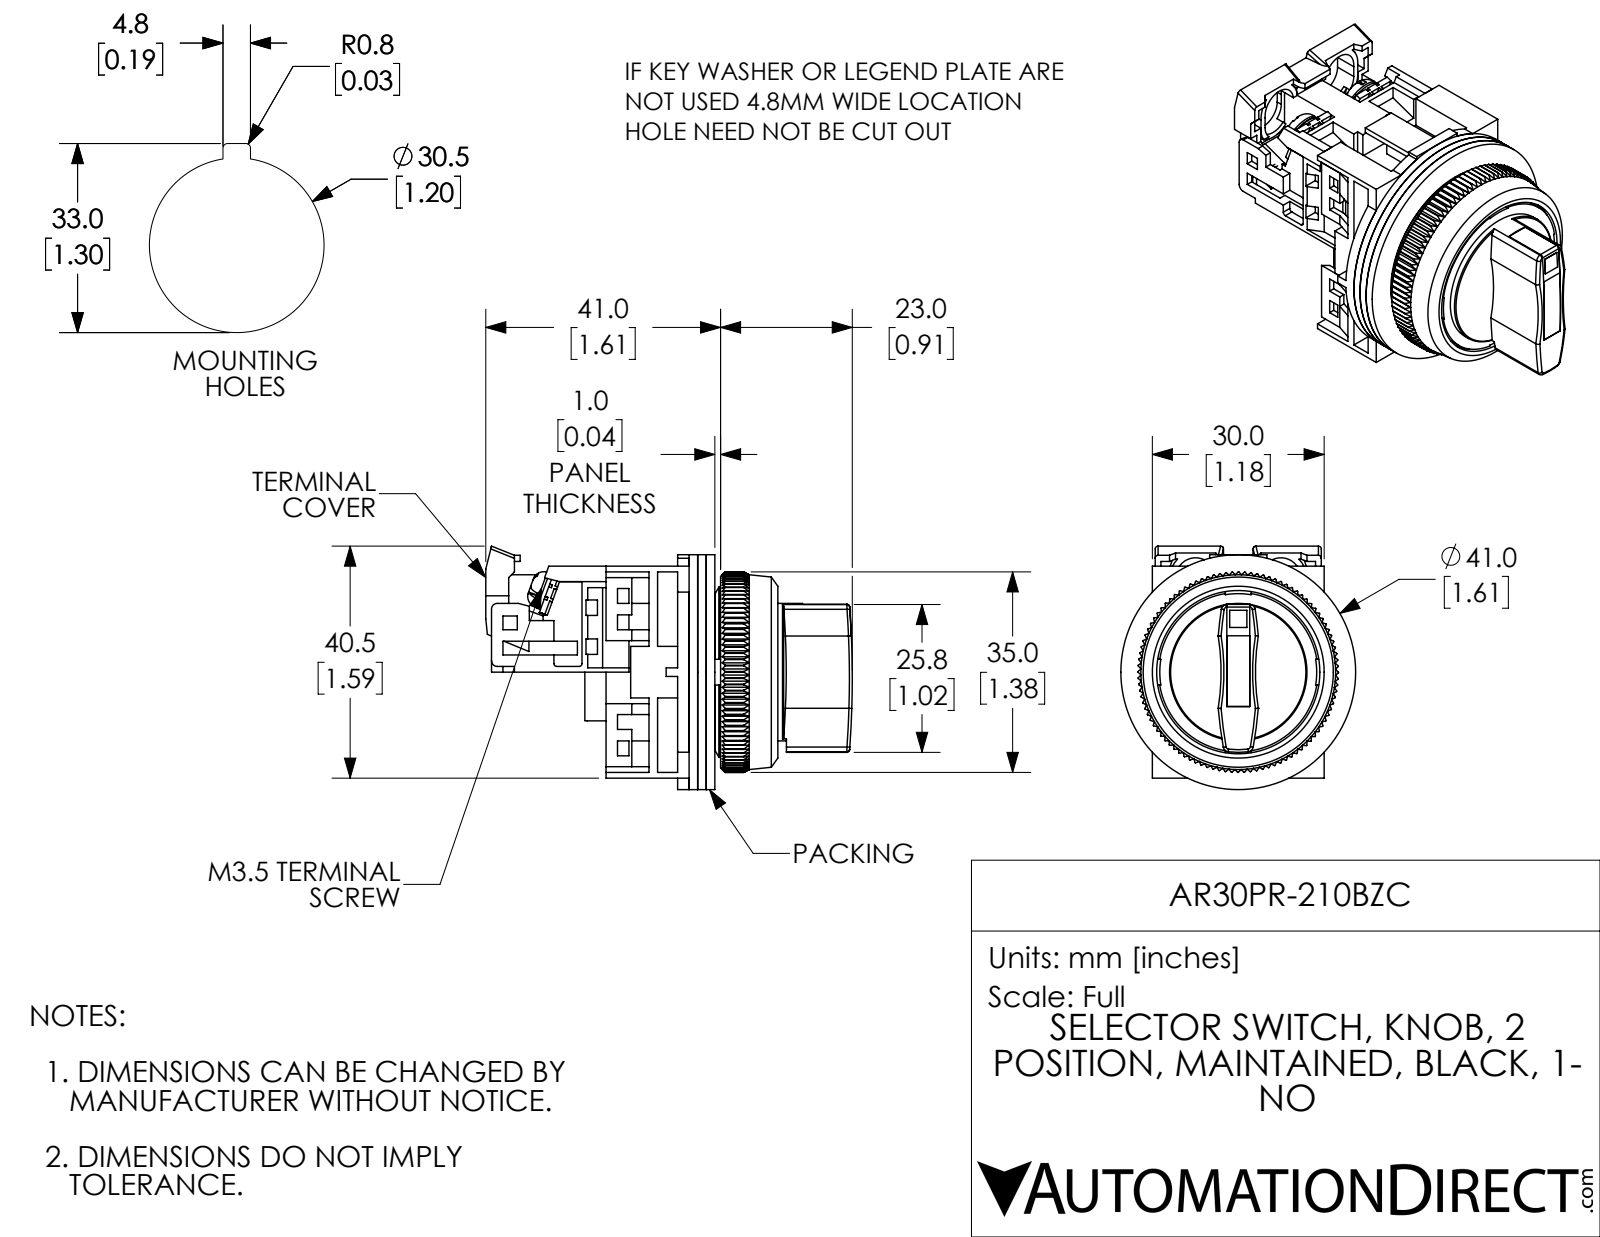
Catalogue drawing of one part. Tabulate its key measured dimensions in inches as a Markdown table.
| quantity | value |
| --- | --- |
| part name | AR30PR-210BZC |
| STEP written by | SolidWorks 2017 (AUTOMOTIVE_DESIGN) |
| units | inches |
| bodies | 18 solids, 1327 faces (832 planar, 283 cylindrical, 212 other) |
| overall size | 2.52 × 1.673 × 1.614 |
| volume | 1.842 in³ |
| surface area | 53.12 in² |
| round holes (diameter × count) | 0.138 × 4, 0.142 × 2, 0.118 × 1, 0.315 × 1, 0.472 × 1, 0.48 × 1, 0.512 × 1, 0.819 × 1, 0.945 × 1, 1.122 × 1, 1.252 × 1 |
| round bosses / shafts (diameter × count) | 0.26 × 2, 0.138 × 2, 1.614 × 1, 1.181 × 1, 0.787 × 1, 0.709 × 1, 0.669 × 1, 0.559 × 1 |
| partial cylindrical surfaces (radius × count) | 0.059 × 8, 0.02 × 7, 0.039 × 6, 0.138 × 2, 0.177 × 2, 1.575 × 2, 1.638 × 2, 2.89 × 2 |
| main face-to-face distances | 0.059, 0.118, 0.177, 0.039, 0.197, 0.079, 0.157, 0.512, 0.689, 0.138 |
| hole center spacings | 0.579, 0.61 |
